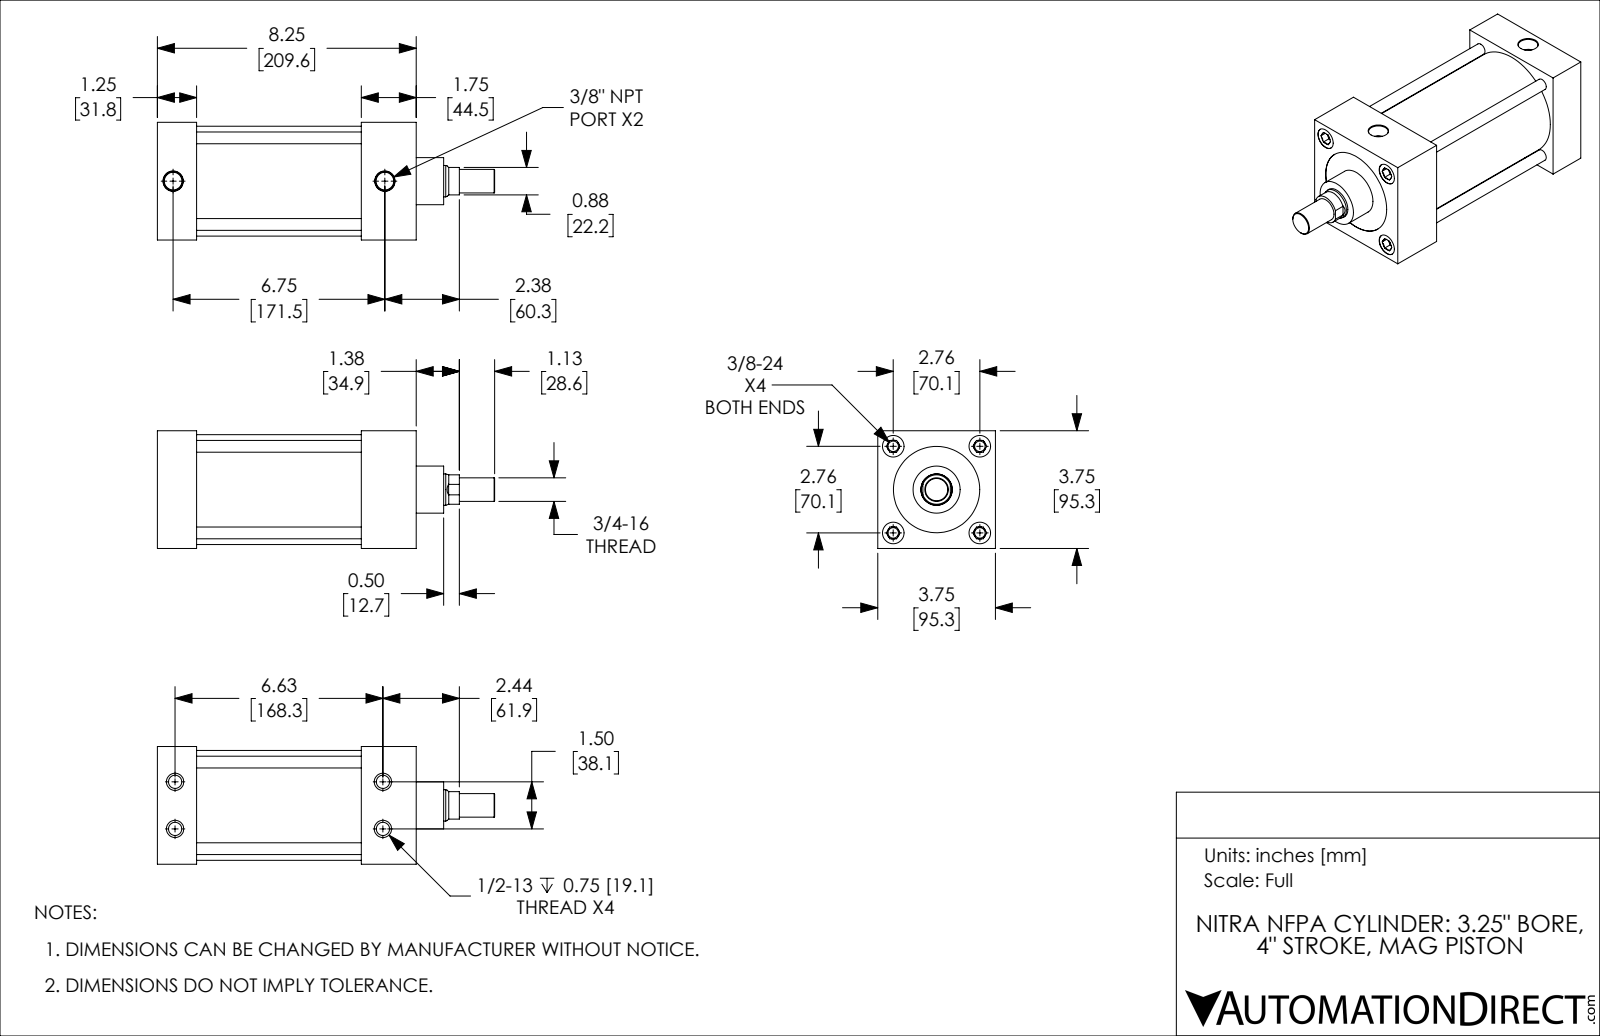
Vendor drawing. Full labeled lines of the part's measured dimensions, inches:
Part name (STEP PRODUCT): D252040DT-M_PISTON_KK1; D252040DT-M; D252040DT-M_BODY
STEP written by: SolidWorks 2019 (CONFIG_CONTROL_DESIGN)
Units: inches
Bodies: 2 solids, 198 faces (58 planar, 62 cylindrical, 78 other)
Overall size (bounding box): 10.75 × 3.75 × 3.75
Volume: 65.15 in³ · Surface area: 317.6 in²
Round holes (diameter × count): ⌀0.332 ×4, ⌀0.422 ×4, ⌀0.687 ×4, ⌀0.562 ×2, ⌀1 ×1, ⌀2.75 ×1, ⌀3.251 ×1
Round bosses / shafts (diameter × count): ⌀0.375 ×4, ⌀3.501 ×1, ⌀3.249 ×1, ⌀1.5 ×1, ⌀0.999 ×1, ⌀0.75 ×1
Partial cylindrical surfaces — rounded edges, fillets, slot ends (radius × count): R0.469 ×1
Main face-to-face distances: 1.25, 3.75, 6.5, 5.25, 2.5, 4, 8.25, 7, 5.75, 1.75
Hole centre spacings: 0.753, 1.952, 2.76, 6.729, 1.5, 3.903, 6.625, 6.793
